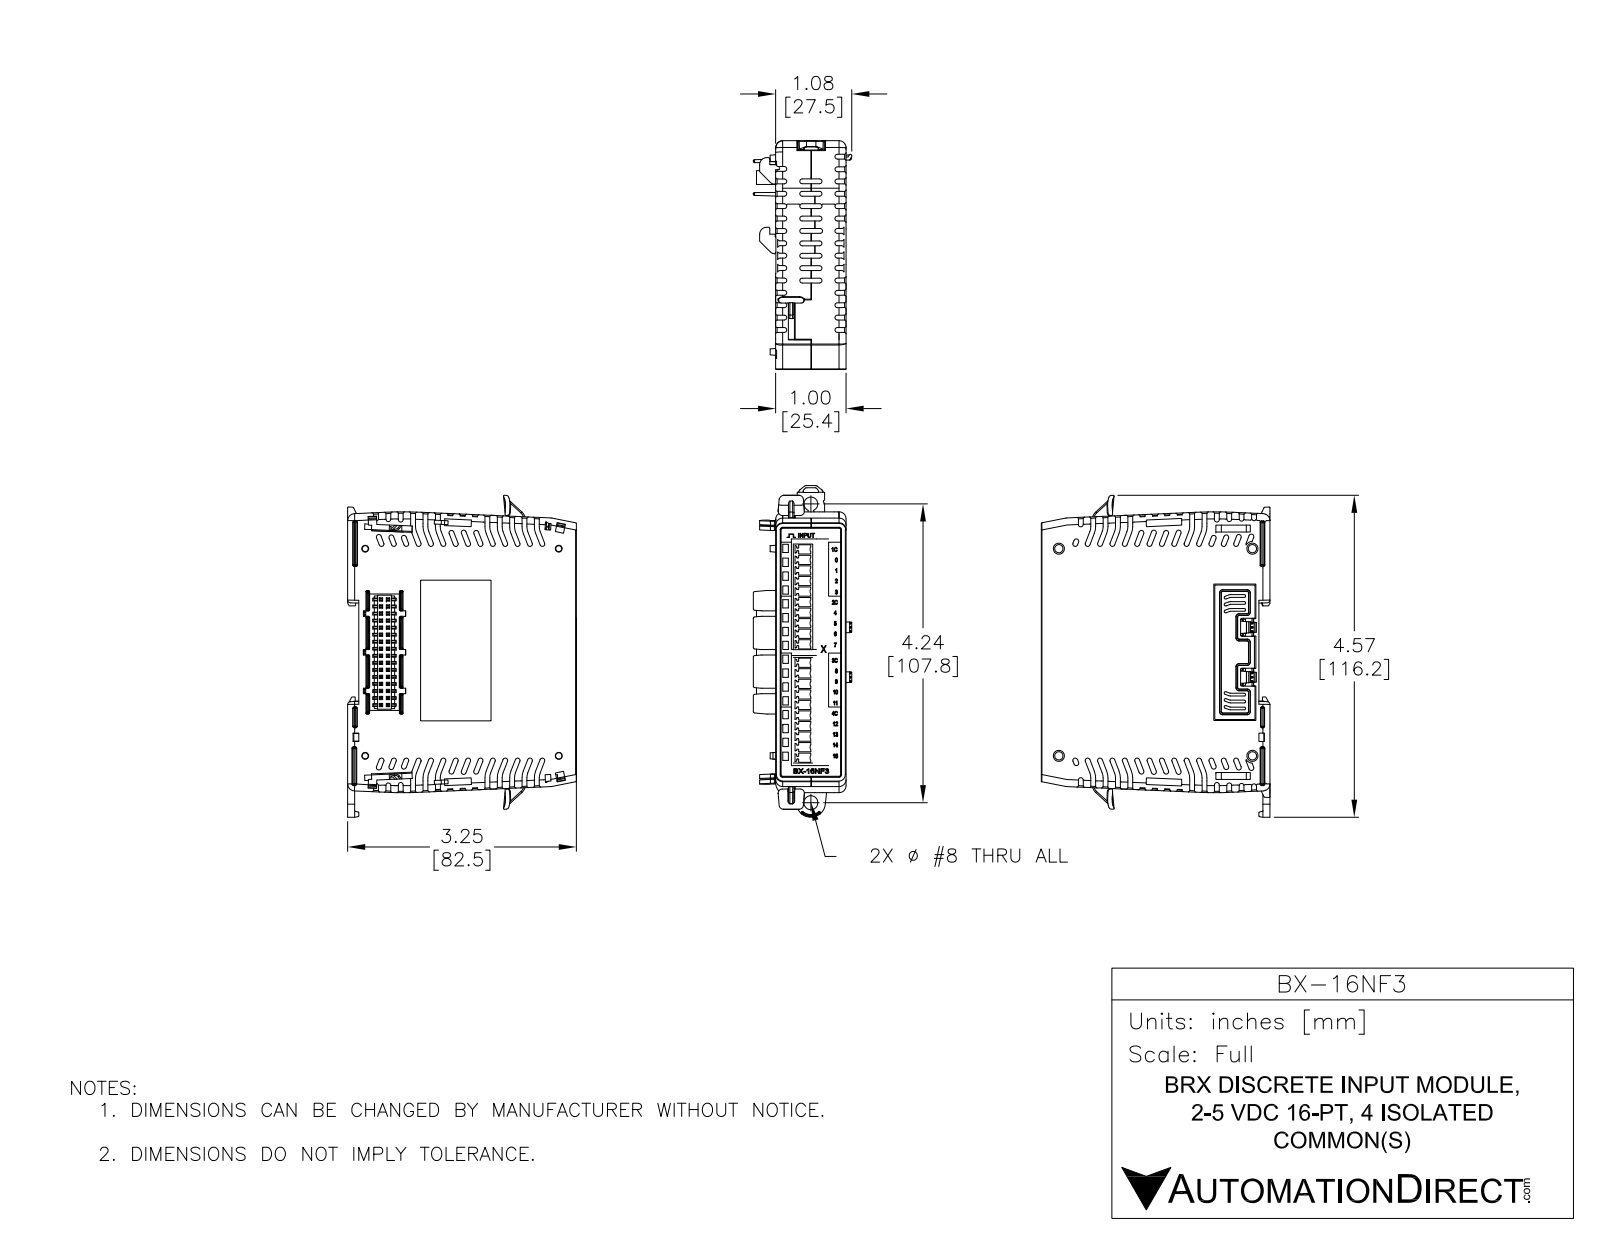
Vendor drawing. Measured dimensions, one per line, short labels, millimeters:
name: BX-16NF3 door mod comb1 fXT c
written by: SolidWorks 2017 (AUTOMOTIVE_DESIGN)
unit: mm
bodies: 14 solids, 3866 faces (2884 planar, 477 cylindrical, 505 other)
size: 116.5 × 82.6 × 35.8
volume: 189 800 mm³; area: 46 600 mm²
holes: 2× ⌀1.2, 2× ⌀1.7, 2× ⌀3, 2× ⌀3, 1× ⌀5.1
bosses: 2× ⌀1.6, 2× ⌀1.5
rounds: 101× R0.2, 46× R0.3, 24× R0.1, 22× R0.5, 20× R1.6, 14× R3, 13× R1, 12× R0.3
face distances: 25.4, 81.6, 81.8, 0.8, 12.1, 16, 1, 4, 77.5, 77.8
hole spacings: 2.5, 20.9, 23.3, 33, 53.2, 55.7, 65.7, 66.5
